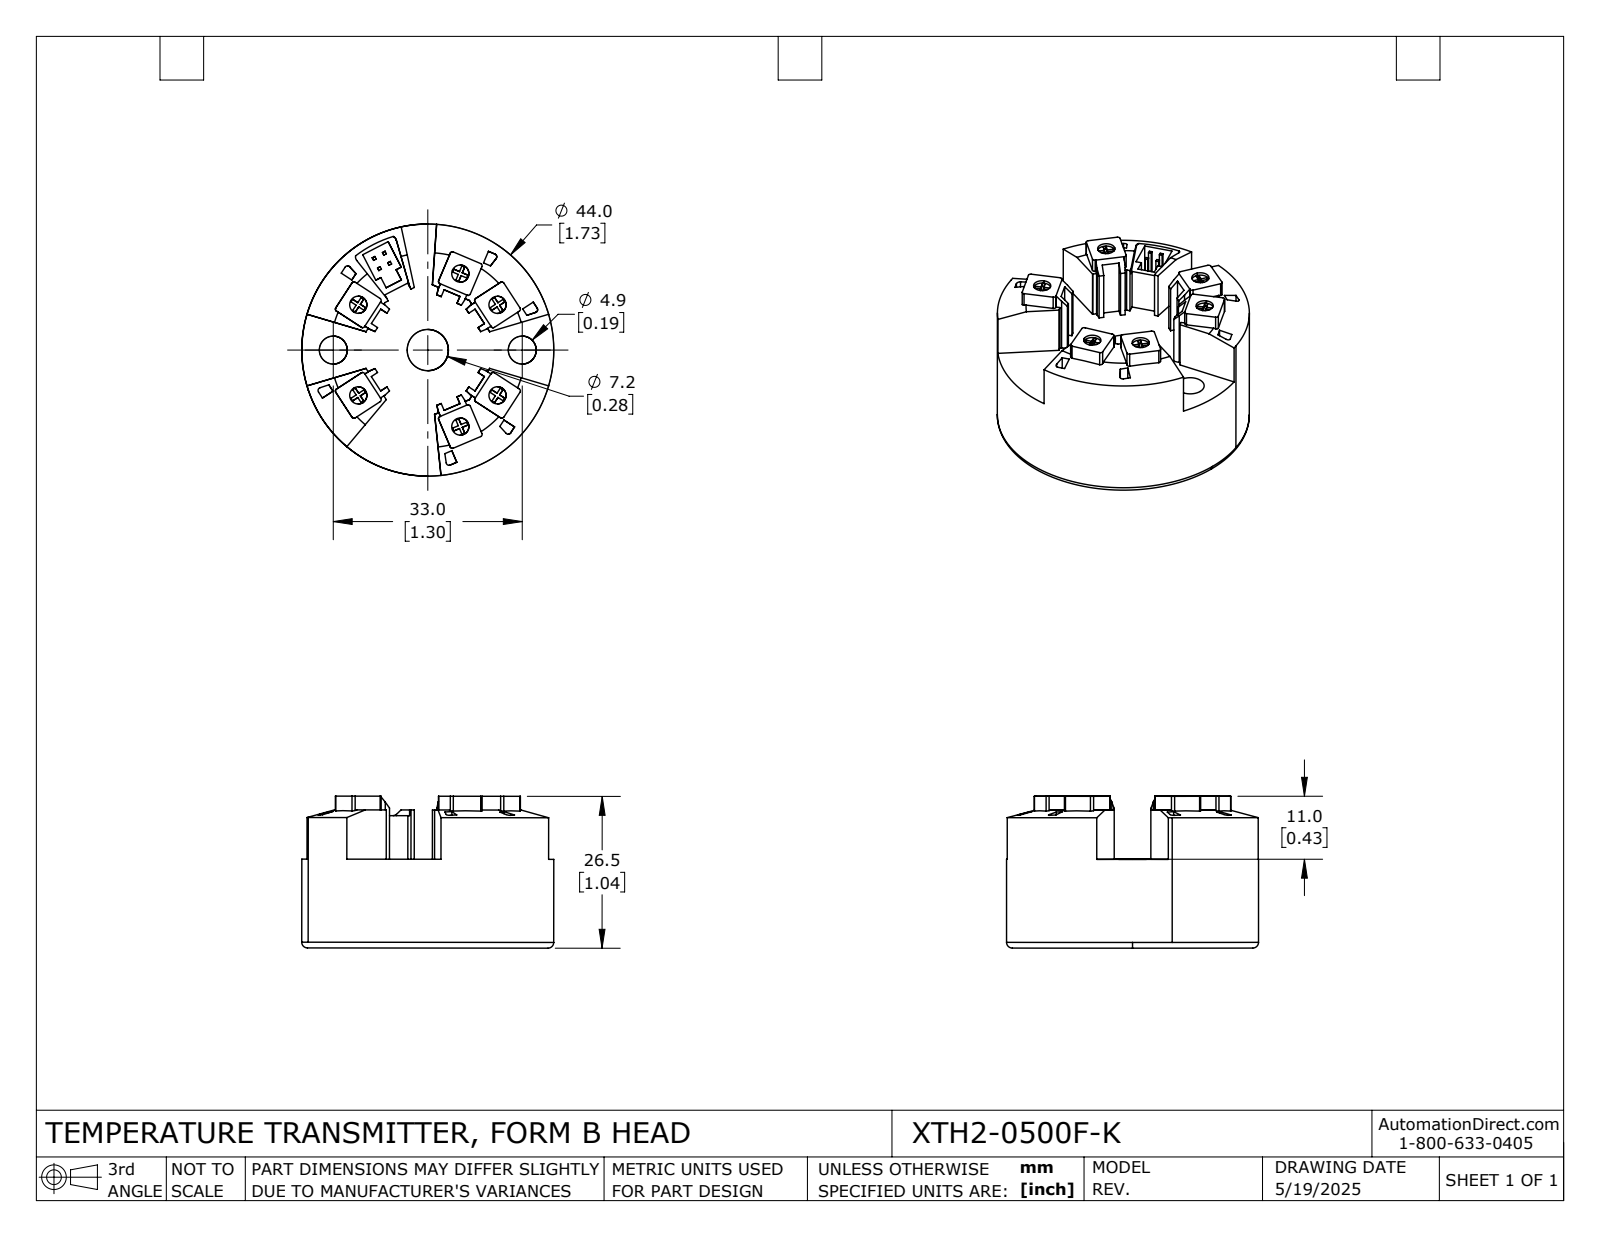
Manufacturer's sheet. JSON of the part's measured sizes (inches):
{"part_name": "XTDH2-0500F-K", "step_written_by": "SolidWorks 2024 (AUTOMOTIVE_DESIGN)", "units": "inches", "bodies": {"solids": 1, "faces": 341, "planar": 281, "cylindrical": 52, "other": 8}, "overall_size": [1.733, 1.732, 1.045], "volume_in3": 1.748, "surface_area_in2": 13.46, "round_holes": [[0.118, 6], [0.193, 2], [0.283, 1]], "round_bosses_or_shafts": [[1.732, 1]], "partial_cylinders_radius": [[0.016, 24], [0.02, 6], [0.039, 2]], "face_to_face_distances": [0.61, 1.043, 0.433, 0.059, 0.177, 0.039, 0.02, 0.118, 0.949, 0.339], "hole_center_spacings": [0.571, 0.333, 0.355, 0.356, 0.65, 0.677, 0.733, 0.875]}
